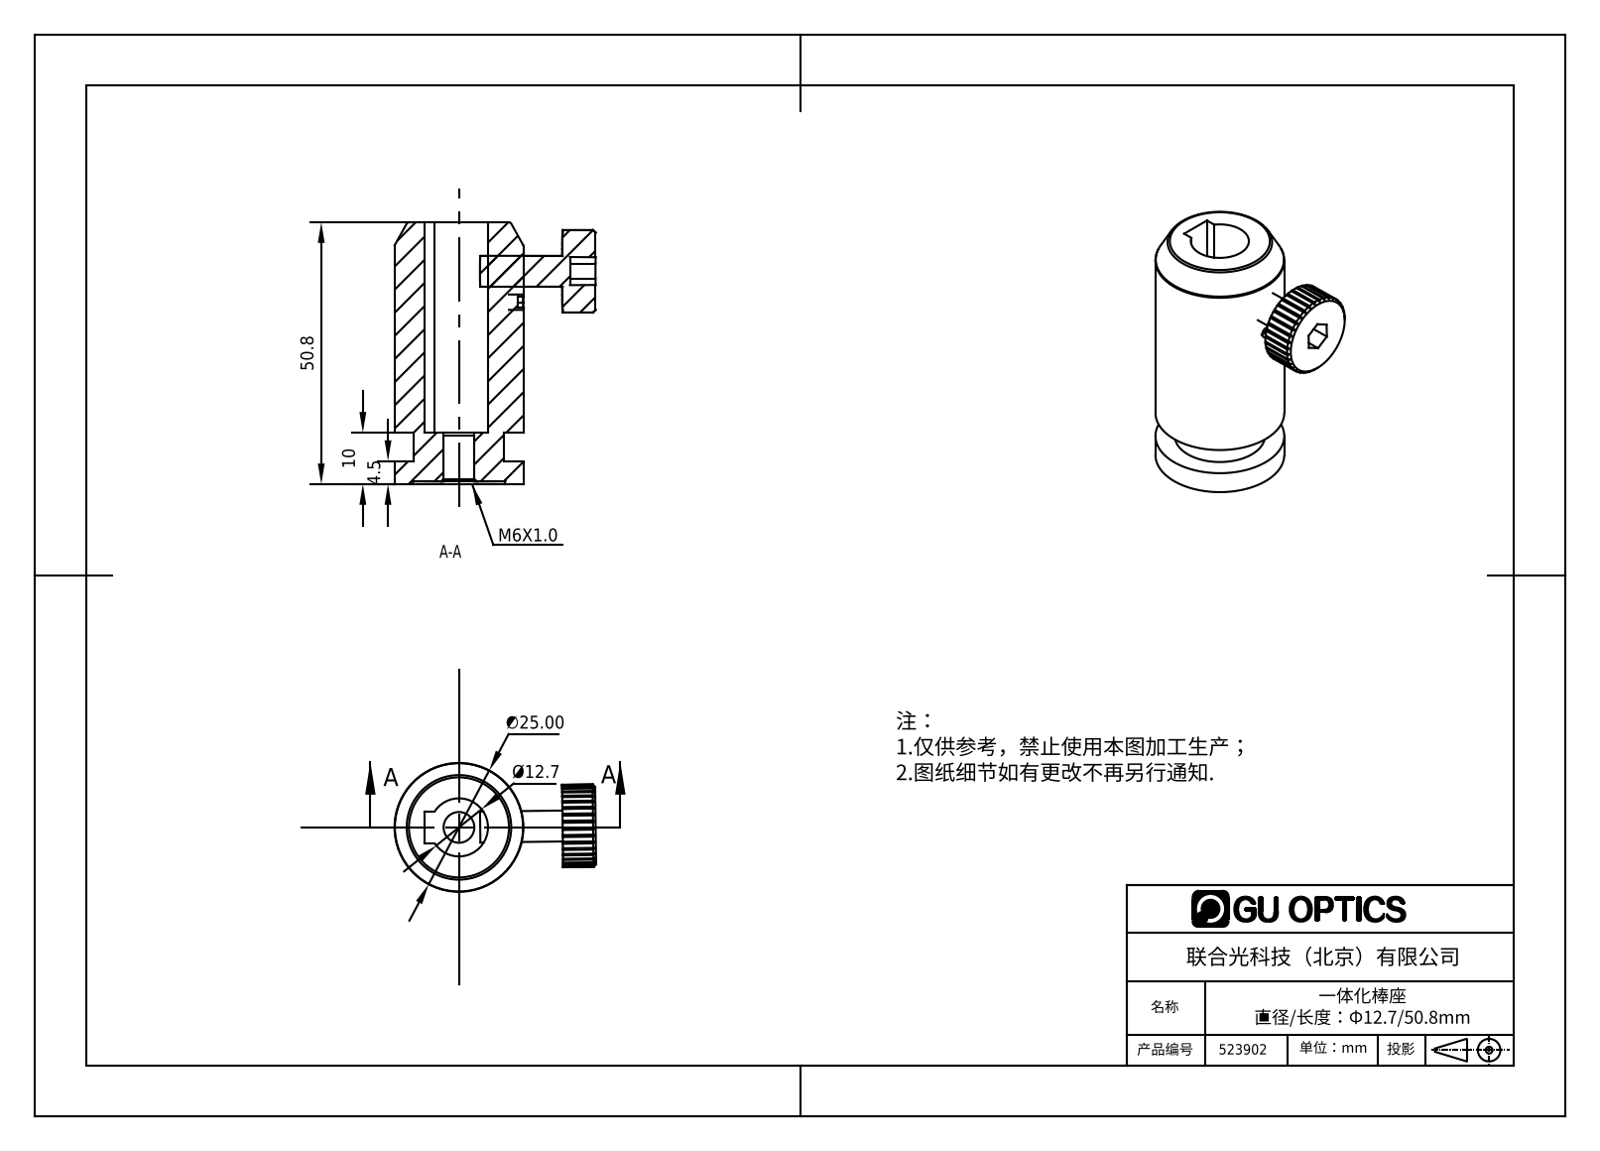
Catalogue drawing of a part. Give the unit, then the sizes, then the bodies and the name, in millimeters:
Units: millimetres
Overall size (bounding box): 50.8 × 39.12 × 25
Round holes (diameter × count): ⌀5.97 ×1, ⌀11.27 ×1, ⌀18 ×1
Round bosses / shafts (diameter × count): ⌀6 ×2, ⌀25 ×1, ⌀17.5 ×1, ⌀3 ×1
Partial cylindrical surfaces — rounded edges, fillets, slot ends (radius × count): R8 ×1
Main face-to-face distances: 5.5, 4.5, 10, 0.5, 4, 9.5, 50.8, 50.3, 46.3, 40.8
Bodies: 0 solids, 176 faces (106 planar, 56 cylindrical, 14 other)
Part name (STEP PRODUCT): 523902
STEP written by: SolidWorks 2016 (AUTOMOTIVE_DESIGN)
